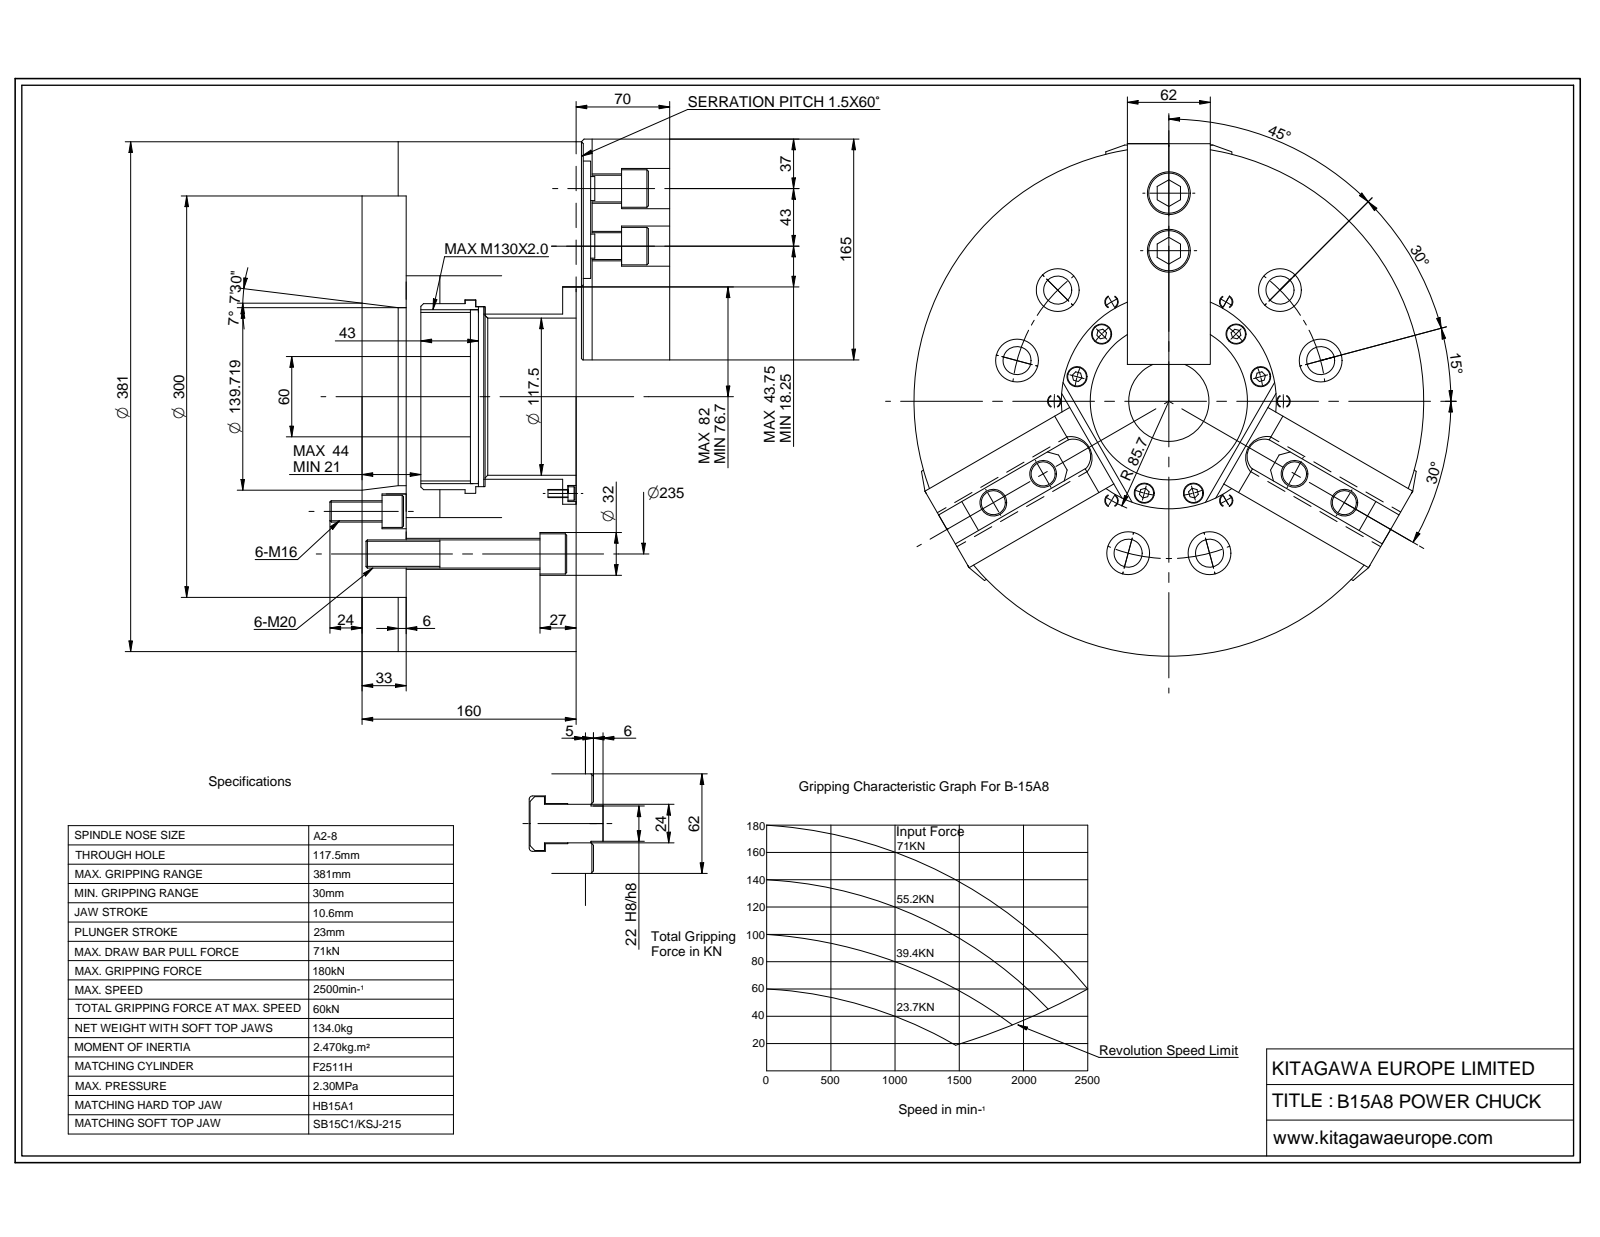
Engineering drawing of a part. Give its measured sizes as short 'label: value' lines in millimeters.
name: B15A08_FULL_ASY2
written by: ST-DEVELOPER v16.7 (AUTOMOTIVE_DESIGN)
unit: mm
bodies: 43 solids, 5192 faces (4439 planar, 349 cylindrical, 404 other)
size: 396.25 × 386.77 × 230.2
volume: 16 120 000 mm³; area: 1 593 000 mm²
holes: 12× ⌀11, 12× ⌀17, 12× ⌀21, 12× ⌀32, 10× ⌀5, 10× ⌀6, 9× ⌀8.38, 9× ⌀10, 6× ⌀4.92, 6× ⌀6.6, 6× ⌀17.29, 6× ⌀20
bosses: 12× ⌀30, 6× ⌀20, 6× ⌀16, 6× ⌀10, 1× ⌀381, 1× ⌀189.7, 1× ⌀148, 1× ⌀137
rounds: 12× R0.4, 12× R0.45, 12× R0.8, 6× R0.5, 6× R1, 6× R1.8, 6× R3.1, 6× R5
face distances: 127, 133, 26, 62, 33, 43, 23, 14, 35, 6
hole spacings: 84.5, 22.17, 67.44, 97.89, 104.49, 114.26, 126.84, 128.98
